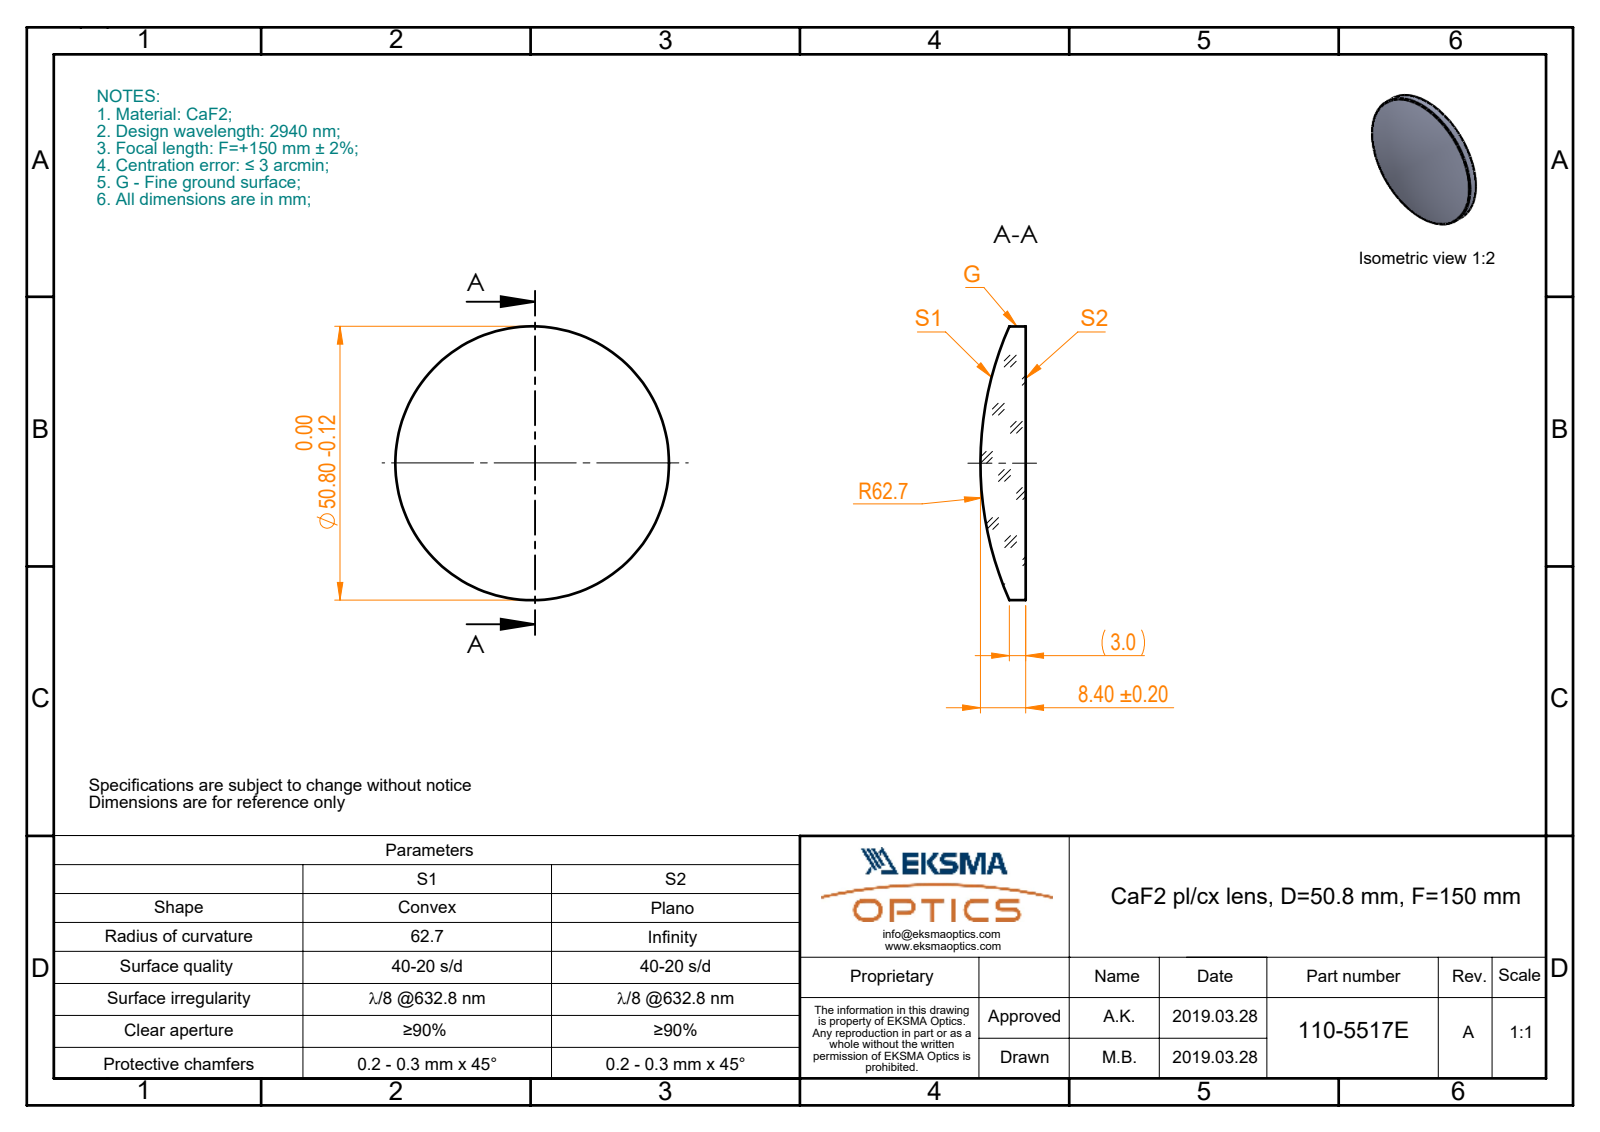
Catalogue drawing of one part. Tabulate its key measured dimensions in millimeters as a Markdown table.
| quantity | value |
| --- | --- |
| part name | 110-5517E CaF2 pl-cx 50.8 F150 |
| STEP written by | SolidWorks 2017 (CONFIG_CONTROL_DESIGN) |
| units | millimeters |
| bodies | 1 solid, 5 faces (1 planar, 2 cylindrical, 2 other) |
| overall size | 50.8 × 50.8 × 8.4 |
| volume | 11 663 mm³ |
| surface area | 4 628 mm² |
| round bosses / shafts (diameter × count) | 50.8 × 1 |
